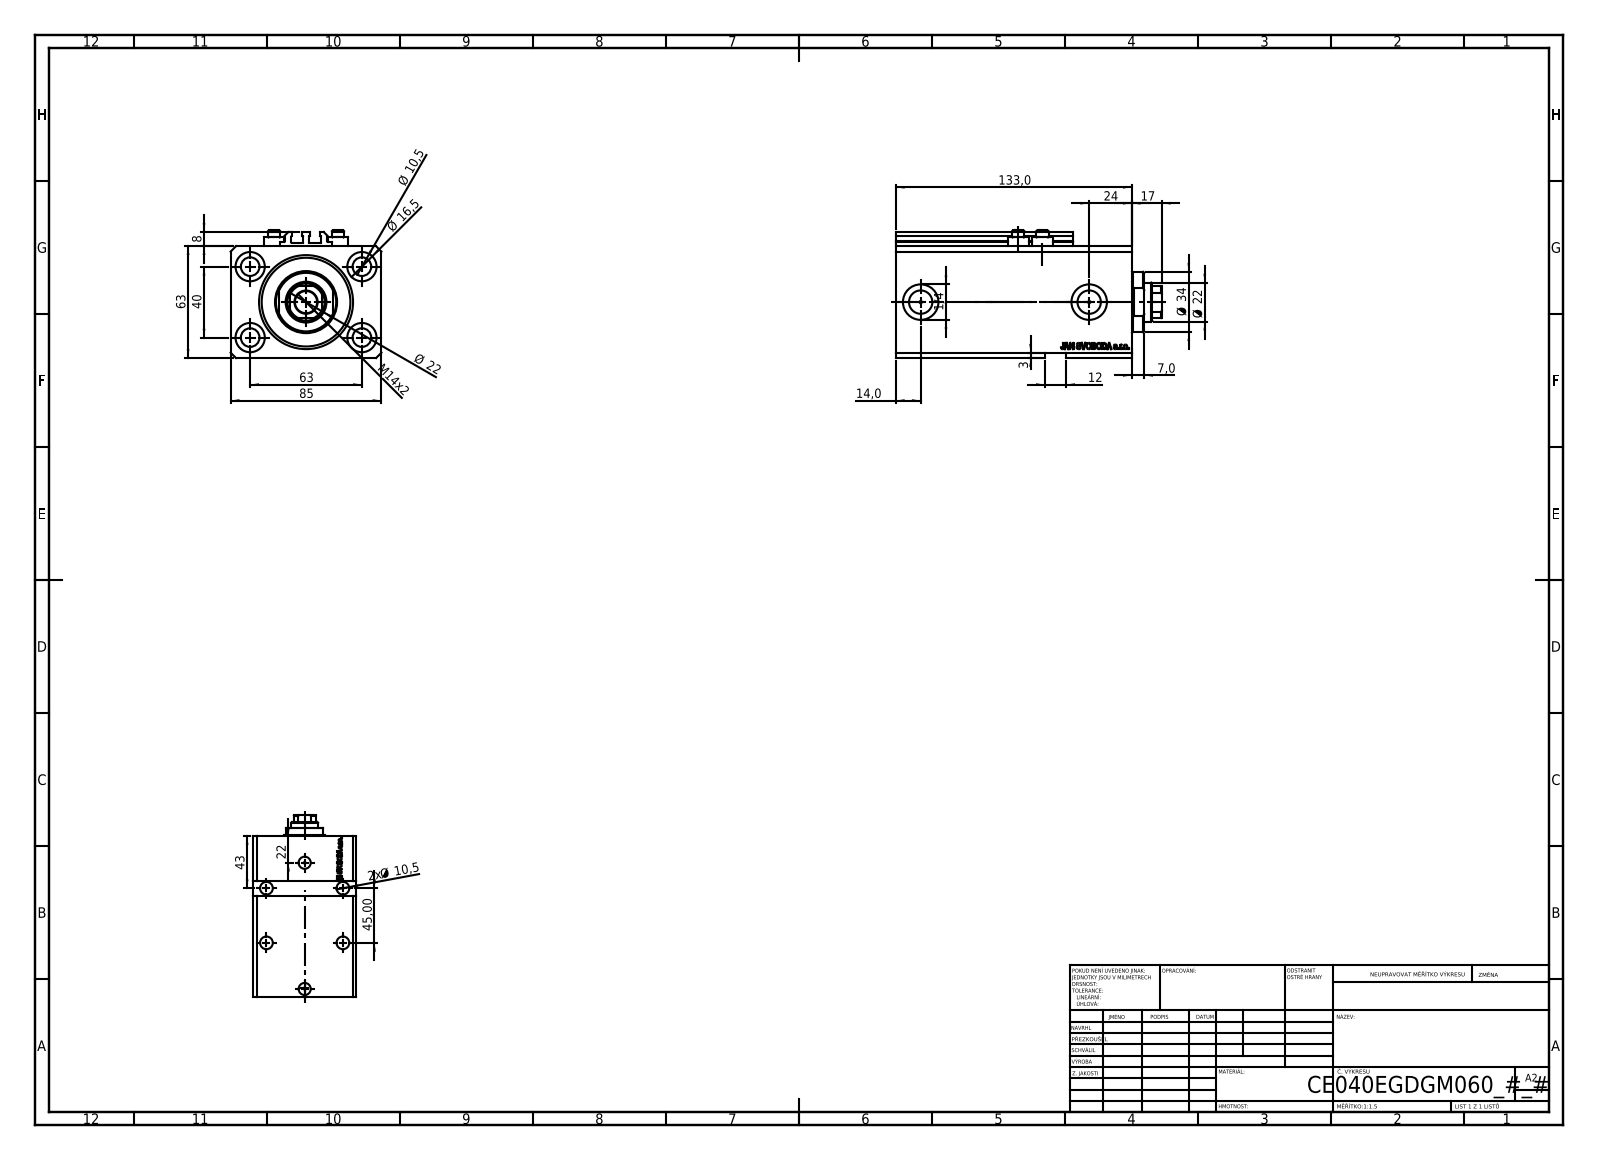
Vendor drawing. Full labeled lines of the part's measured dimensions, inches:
Part name (STEP PRODUCT): V250CE_C_VCP; V250CE_VC_E; ALLEN BOLT V250CE; V250CE_E_Body
STEP written by: SolidWorks 2019 (CONFIG_CONTROL_DESIGN)
Units: inches
Bodies: 8 solids, 1123 faces (539 planar, 158 cylindrical, 426 other)
Overall size (bounding box): 5.906 × 3.346 × 2.835
Volume: 36.33 in³ · Surface area: 197.9 in²
Round holes (diameter × count): ⌀0.413 ×8, ⌀0.049 ×4, ⌀0.157 ×4, ⌀0.65 ×4, ⌀0.394 ×2, ⌀0.518 ×2, ⌀0.787 ×2, ⌀0.492 ×1, ⌀0.866 ×1, ⌀1.575 ×1, ⌀2.087 ×1
Round bosses / shafts (diameter × count): ⌀0.457 ×4, ⌀0.276 ×4, ⌀1.339 ×1
Partial cylindrical surfaces — rounded edges, fillets, slot ends (radius × count): R0.008 ×10, R0.413 ×1
Main face-to-face distances: 2.48, 3.346, 5.236, 0.669, 4.567, 0.449, 4.118, 4.787, 0.118, 2.559
Hole centre spacings: 1.469, 2.48, 0.535, 0.606, 0.983, 1.084, 1.324, 1.417
